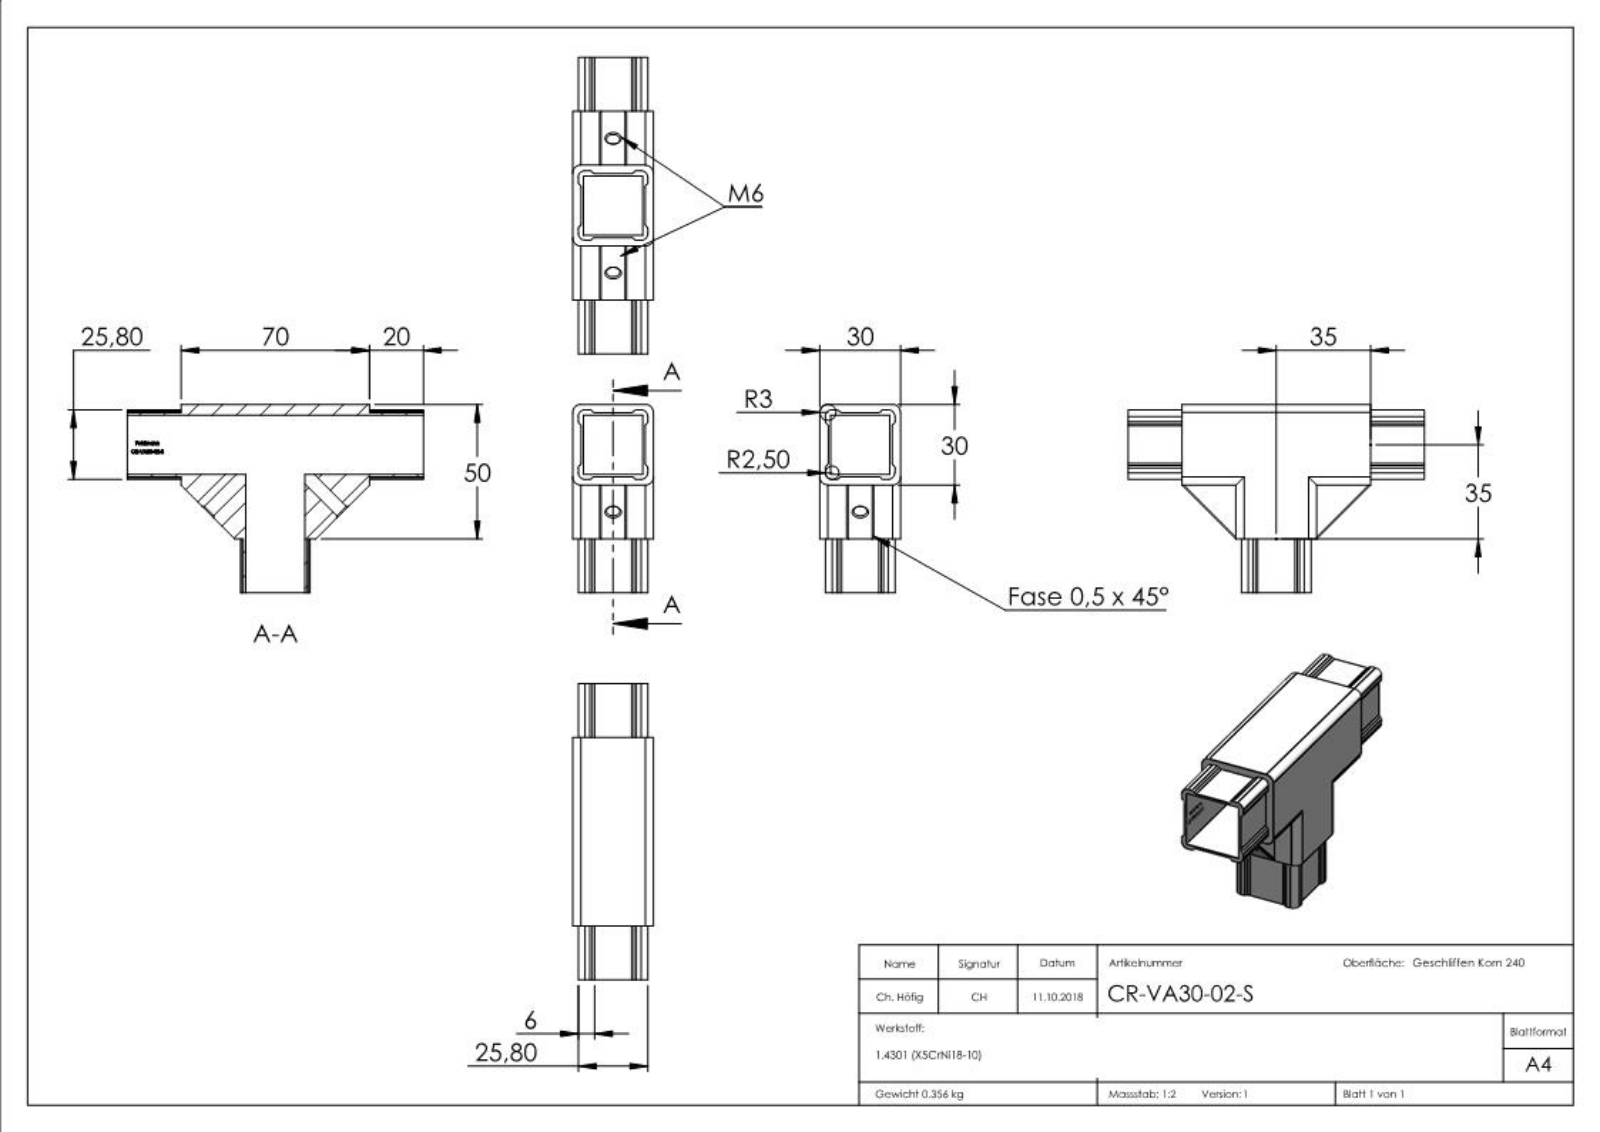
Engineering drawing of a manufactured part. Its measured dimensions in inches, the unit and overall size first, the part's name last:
Units: inches
Overall size (bounding box): 4.331 × 2.756 × 1.181
Round holes (diameter × count): ⌀0.197 ×2
Partial cylindrical surfaces — rounded edges, fillets, slot ends (radius × count): R0.039 ×32, R0.098 ×8, R0.118 ×8
Main face-to-face distances: 0.157, 1.024, 0.866, 0.035, 0.122, 1.059, 0.902, 1.181, 0.787, 0.937
Volume: 2.747 in³ · Surface area: 47.95 in²
Bodies: 1 solid, 398 faces (205 planar, 74 cylindrical, 119 other)
Part name (STEP PRODUCT): CR-VA30-02-S
STEP written by: SolidWorks 2015 (CONFIG_CONTROL_DESIGN)
